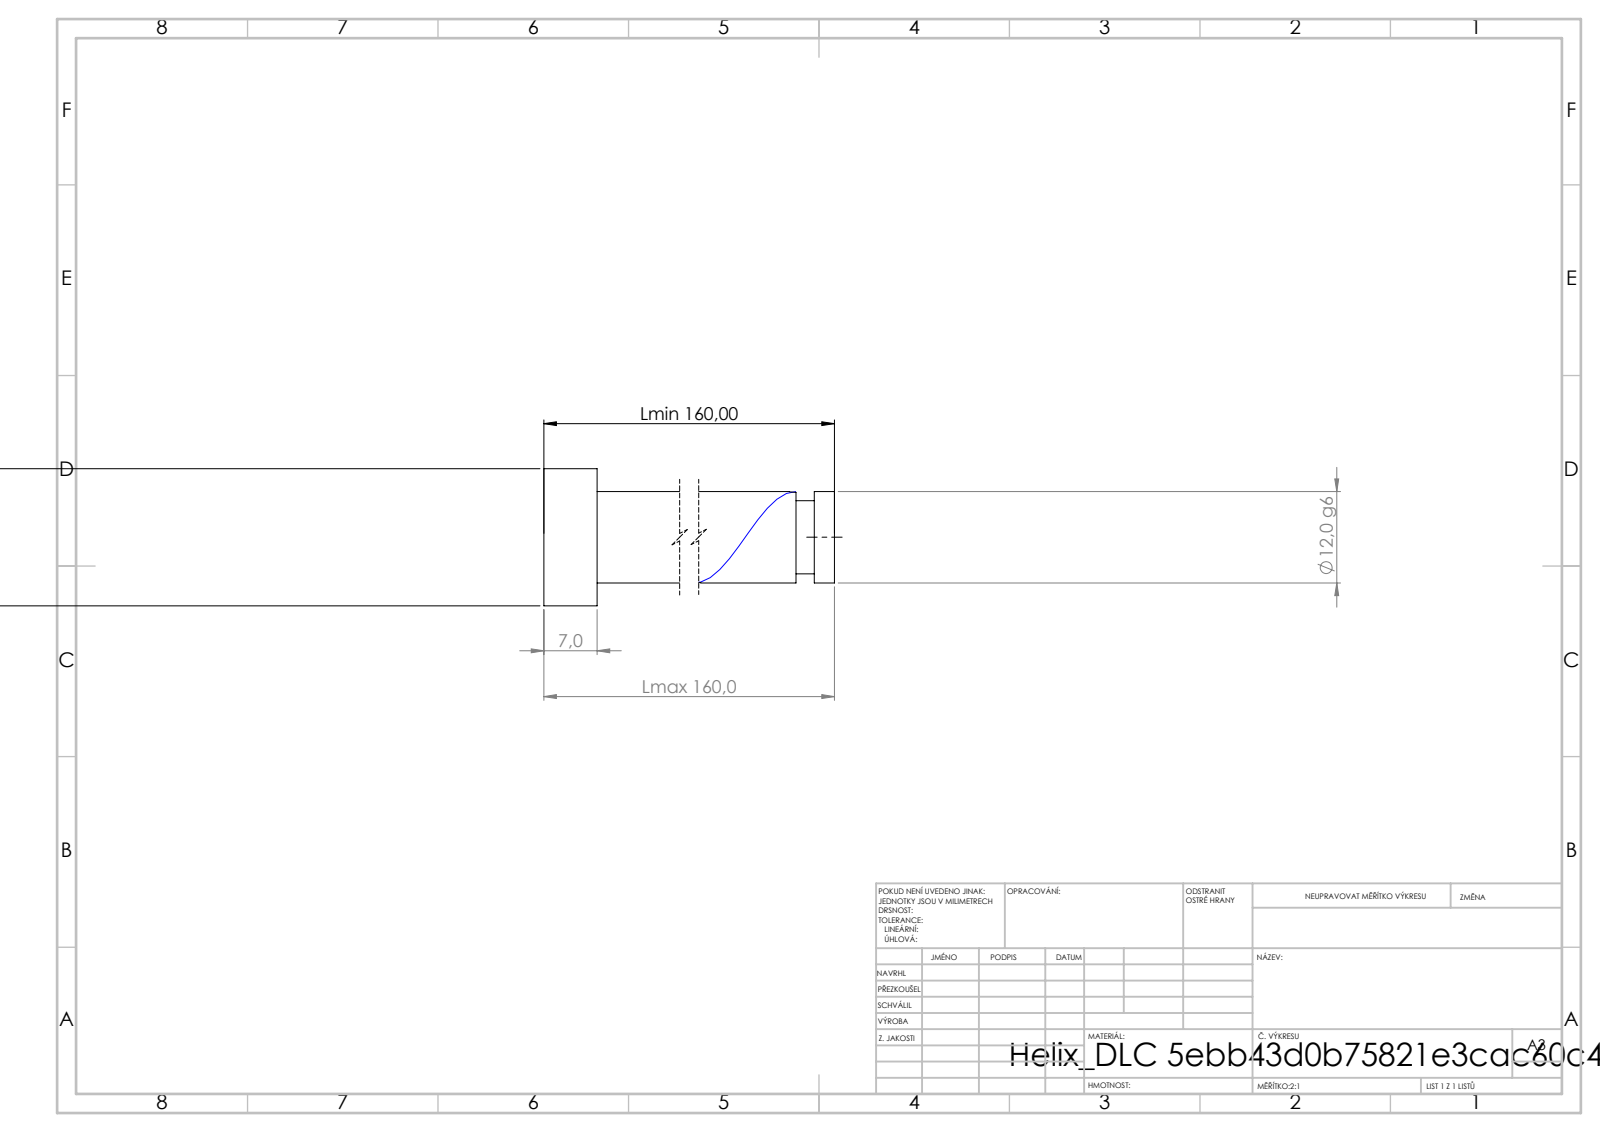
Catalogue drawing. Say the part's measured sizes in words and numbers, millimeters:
Its 3-D file was written by "SolidWorks 2019 (CONFIG_CONTROL_DESIGN)". It is 1 solid with 21 faces: 6 planar, 14 cylindrical and 1 other. Overall it measures 160 by 18 by 18 millimeters. Its volume is 18 814 cubic millimeters and its surface area 6 930 square millimeters. Round bosses or shafts: 1 of diameter 18, 1 of diameter 12, 1 of diameter 9.6. The main face-to-face distances are 7, 160, 153, 157.35, 150.35, 2.65, 154.95, 147.95, 2.4, 5.05.
